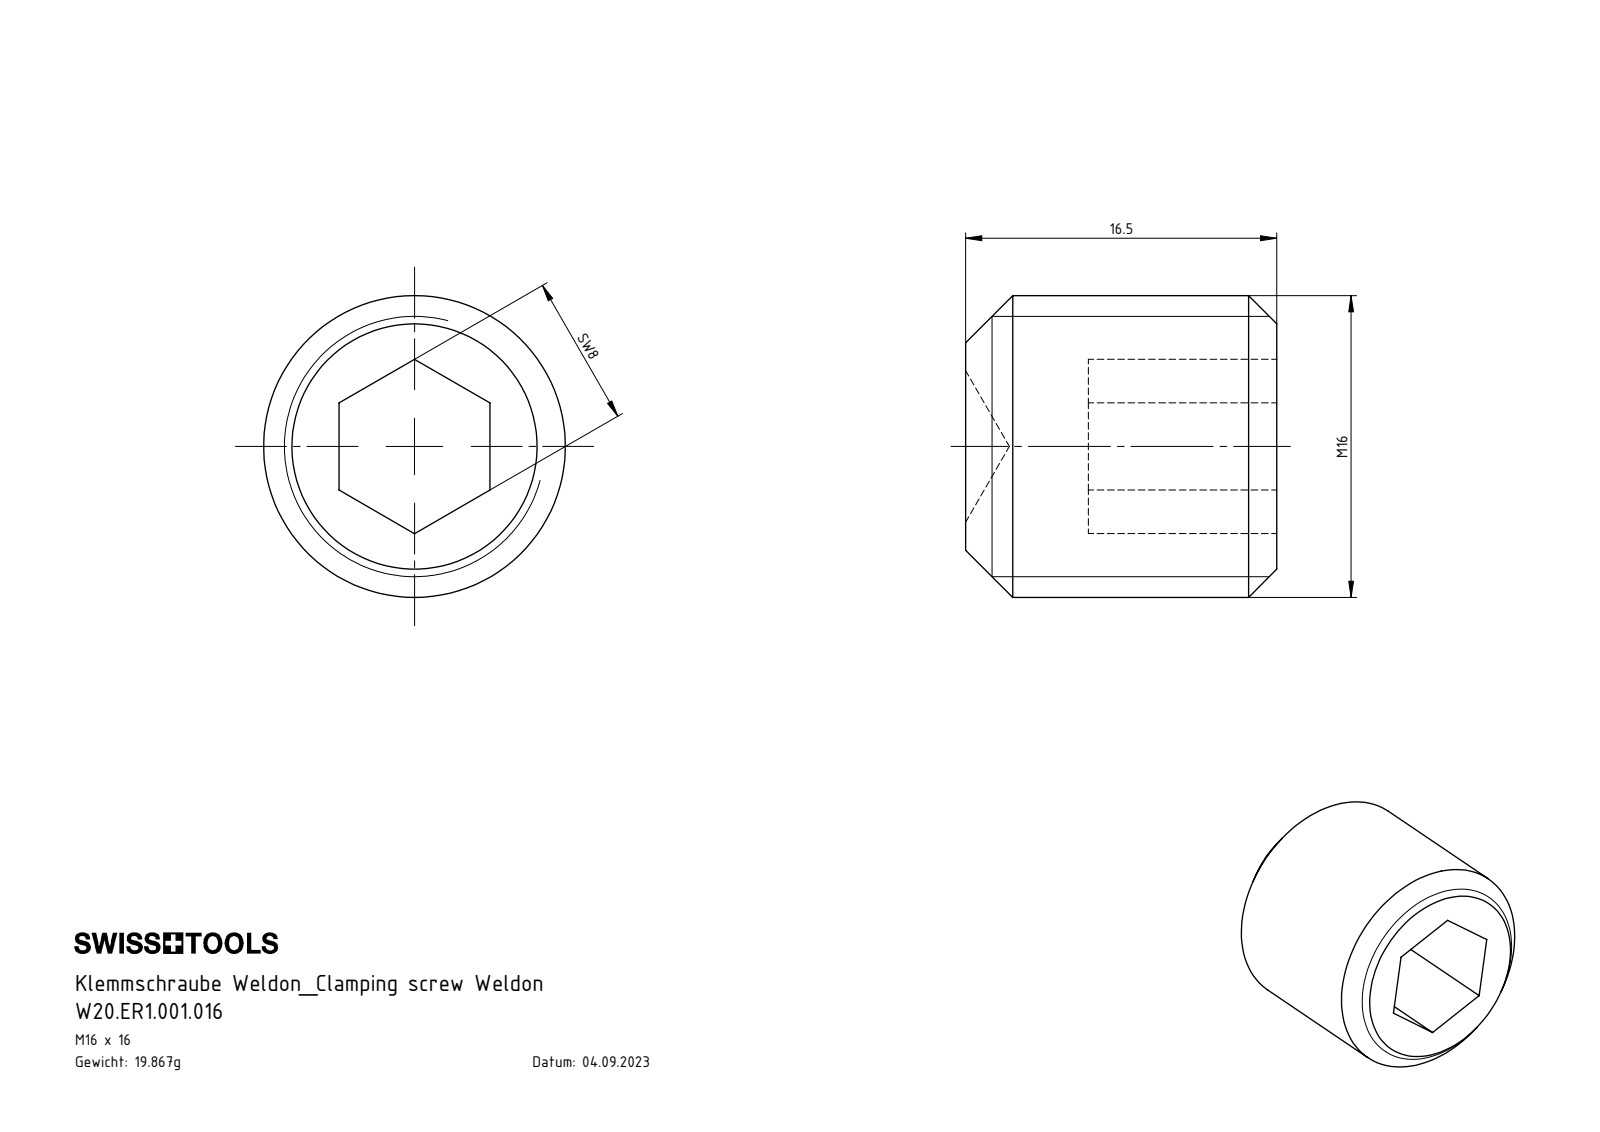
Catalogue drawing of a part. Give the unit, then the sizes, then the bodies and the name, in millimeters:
Units: millimetres
Overall size (bounding box): 16.5 × 16 × 16
Round bosses / shafts (diameter × count): ⌀16 ×1
Main face-to-face distances: 8, 10, 16.5, 6.5
Volume: 2 560 mm³ · Surface area: 1 404 mm²
Bodies: 1 solid, 17 faces (9 planar, 2 cylindrical, 6 other)
Part name (STEP PRODUCT): W20.ER1.001.016
STEP written by: SolidWorks 2017 (AUTOMOTIVE_DESIGN)
